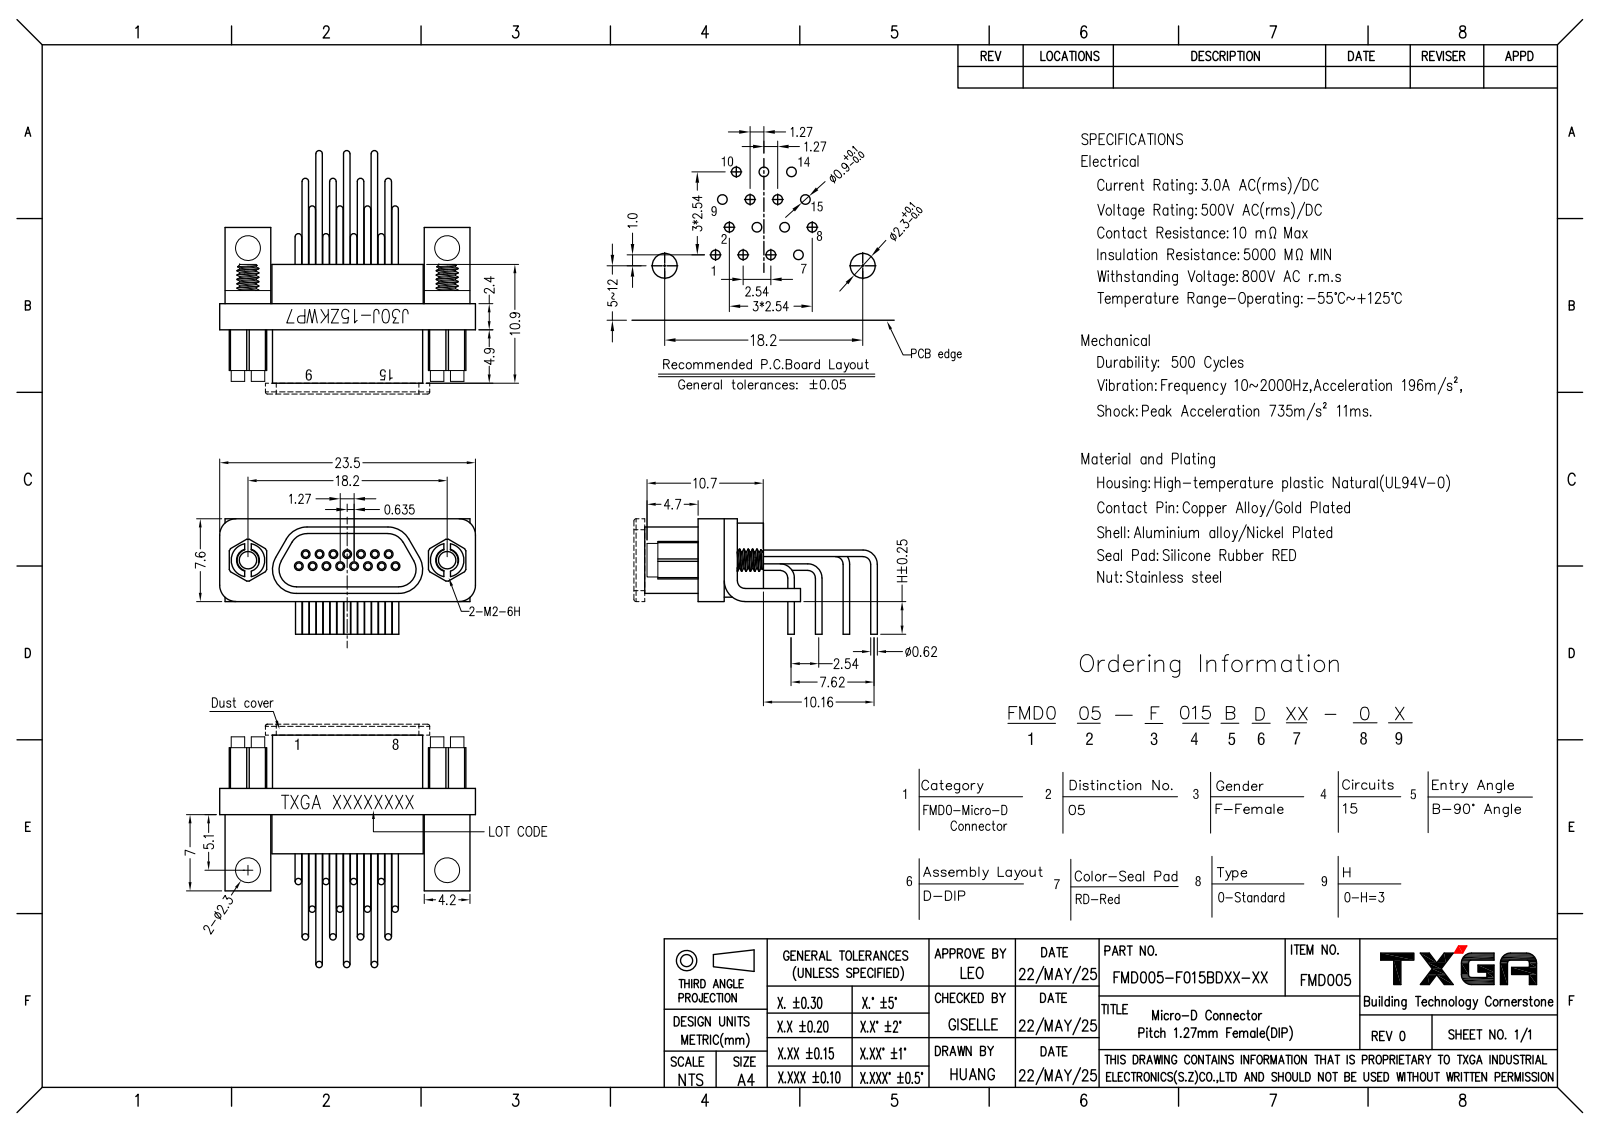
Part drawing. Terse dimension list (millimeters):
name: FMD005-F015BDRD-00
written by: SolidWorks 2021 (CONFIG_CONTROL_DESIGN)
unit: mm
bodies: 1 solid, 1214 faces (587 planar, 266 cylindrical, 361 other)
size: 23.6 × 21.36 × 10.6
volume: 1 129 mm³; area: 1 966 mm²
holes: 15× ⌀0.6, 2× ⌀1.6, 2× ⌀1.8, 2× ⌀2.3
bosses: 15× ⌀0.8, 15× ⌀0.6, 2× ⌀3.1, 2× ⌀2
rounds: 12× R0.3, 4× R1.5, 4× R1.7, 4× R2, 4× R2.4, 2× R1.15, 1× R0.7, 1× R1.9
face distances: 6, 0.7, 3.6, 2.4, 0.75, 1.2, 6.85, 7.2, 1.45, 6.15
hole spacings: 1.27, 2.54, 2.2, 3.81, 1.28, 3.36, 5.08, 6.35
